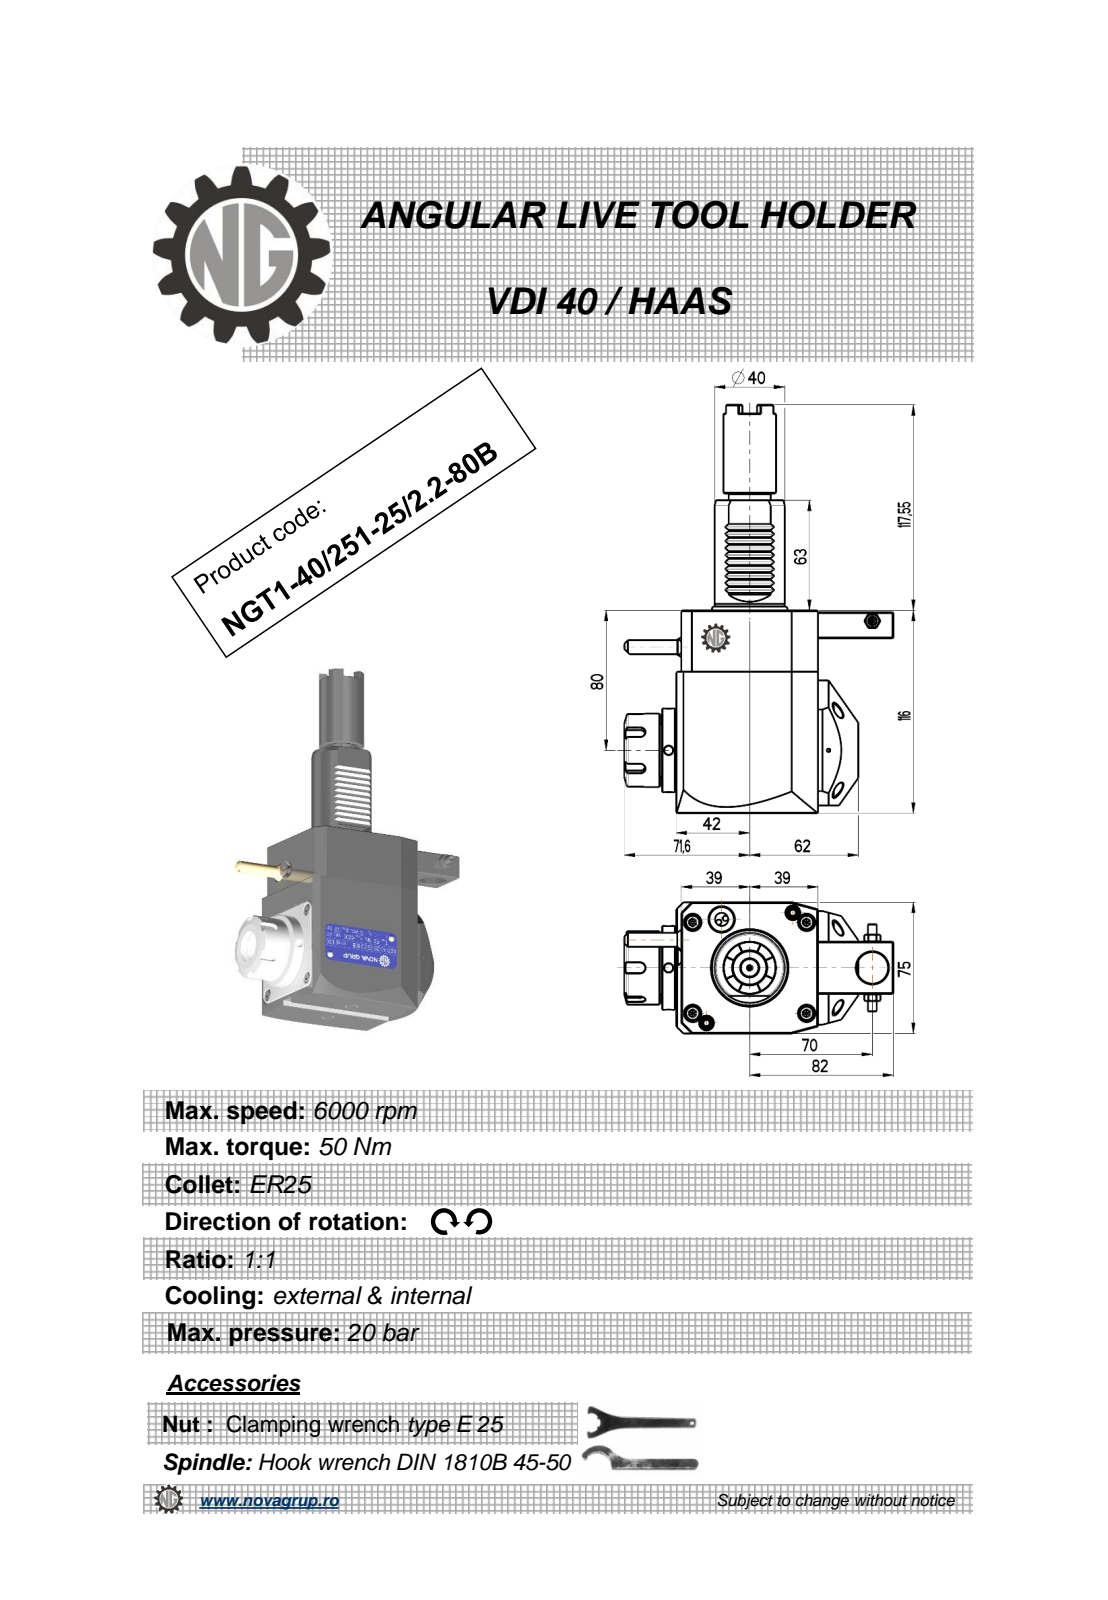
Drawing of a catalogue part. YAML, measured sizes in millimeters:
part_name: "NGT1_40_251_25_2_2_80B"
step_written_by: "PRO/ENGINEER BY PARAMETRIC TECHNOLOGY CORPORATION, 2010280 (CONFIG_CONTROL_DESIGN)"
units: millimeters
bodies: {solids: 1, faces: 476, planar: 223, cylindrical: 94, other: 159}
overall_size: [233.55, 153.6, 76.6]
volume: 914833
surface_area: 77023
round_holes:
  - {diameter: 5, count: 3}
  - {diameter: 3, count: 1}
  - {diameter: 4.2, count: 1}
  - {diameter: 9.5, count: 1}
  - {diameter: 18, count: 1}
  - {diameter: 20.3, count: 1}
round_bosses_or_shafts:
  - {diameter: 48, count: 1}
  - {diameter: 42, count: 1}
  - {diameter: 40, count: 1}
  - {diameter: 37.5, count: 1}
  - {diameter: 33, count: 1}
  - {diameter: 30, count: 1}
  - {diameter: 24, count: 1}
  - {diameter: 10, count: 1}
partial_cylinders:
  - {radius: 0.26, count: 12}
  - {radius: 0.3, count: 10}
  - {radius: 0.2, count: 6}
  - {radius: 3, count: 5}
  - {radius: 0.5, count: 1}
  - {radius: 9.75, count: 1}
  - {radius: 40, count: 1}
face_to_face_distances: [75, 116, 81, 3, 78, 2.8, 80.8, 1, 112, 11]
hole_center_spacings: [20.93, 61.13, 72.5, 116.25, 137.8]
